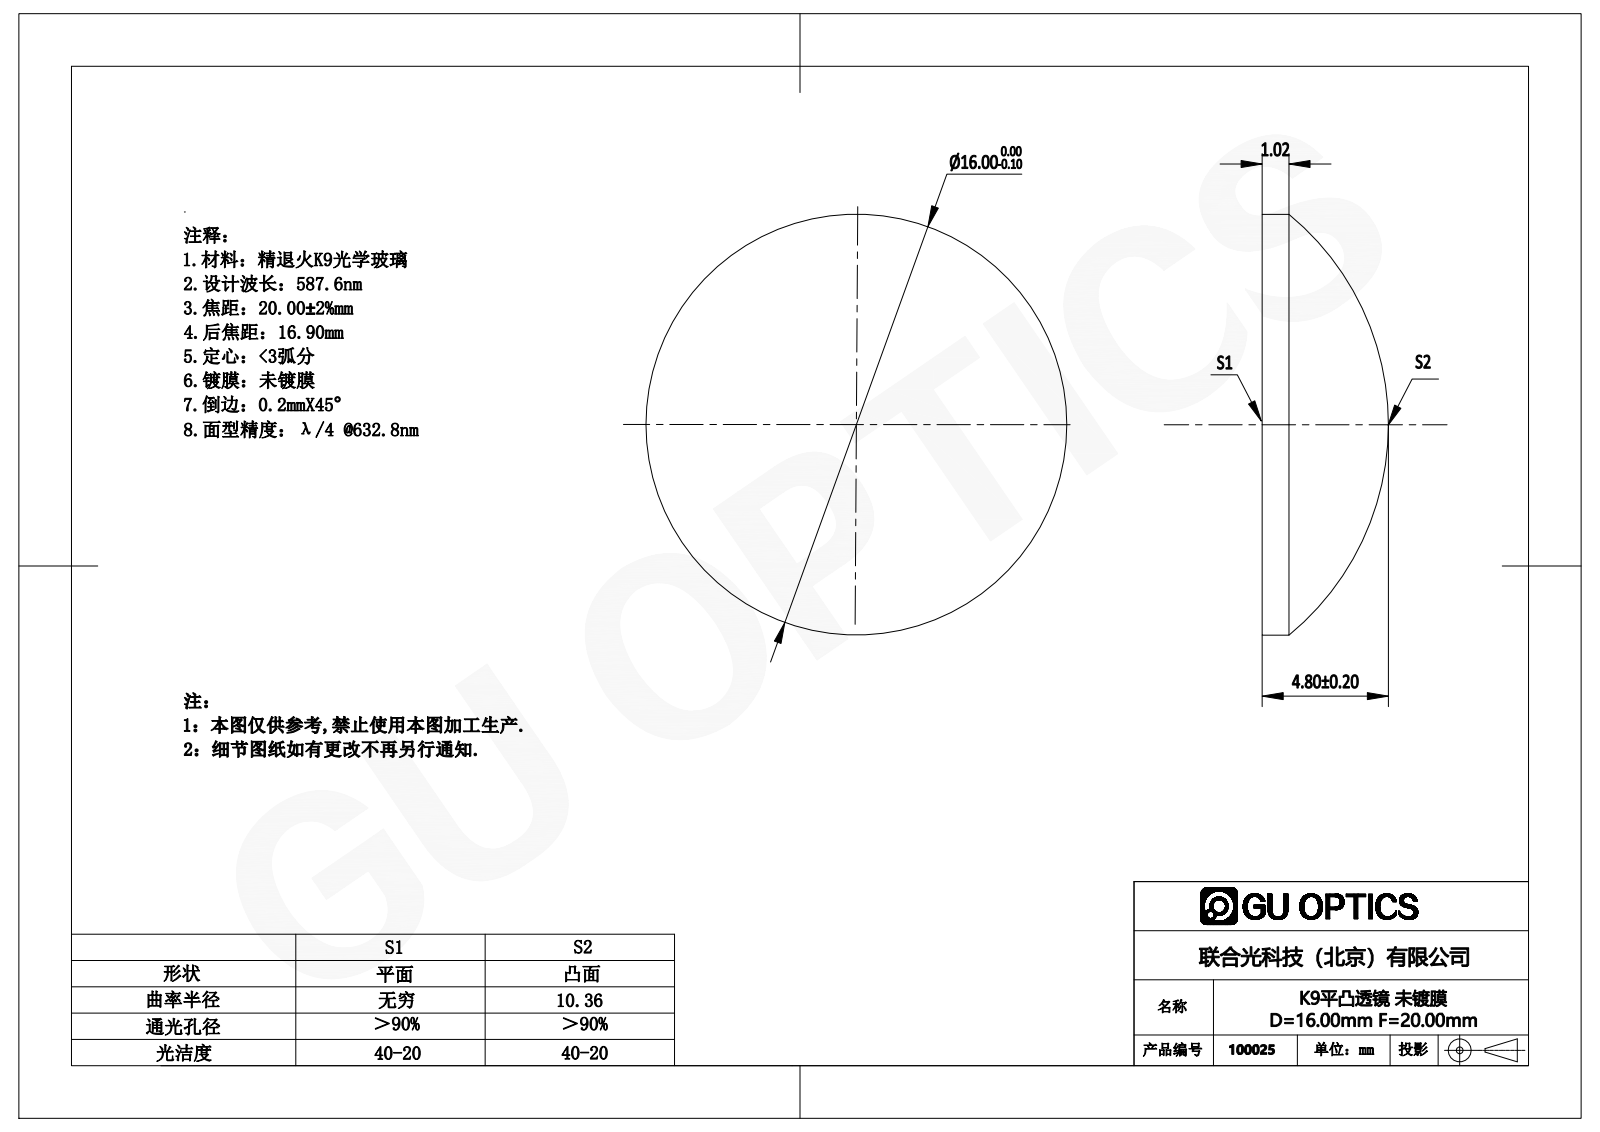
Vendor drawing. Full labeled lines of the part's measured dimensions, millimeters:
Part name (STEP PRODUCT): 100025
STEP written by: SolidWorks 2016 (AUTOMOTIVE_DESIGN)
Units: millimetres
Bodies: 1 solid, 5 faces (1 planar, 2 cylindrical, 2 other)
Overall size (bounding box): 16 × 16 × 4.8
Volume: 613 mm³ · Surface area: 498 mm²
Round bosses / shafts (diameter × count): ⌀16 ×1
